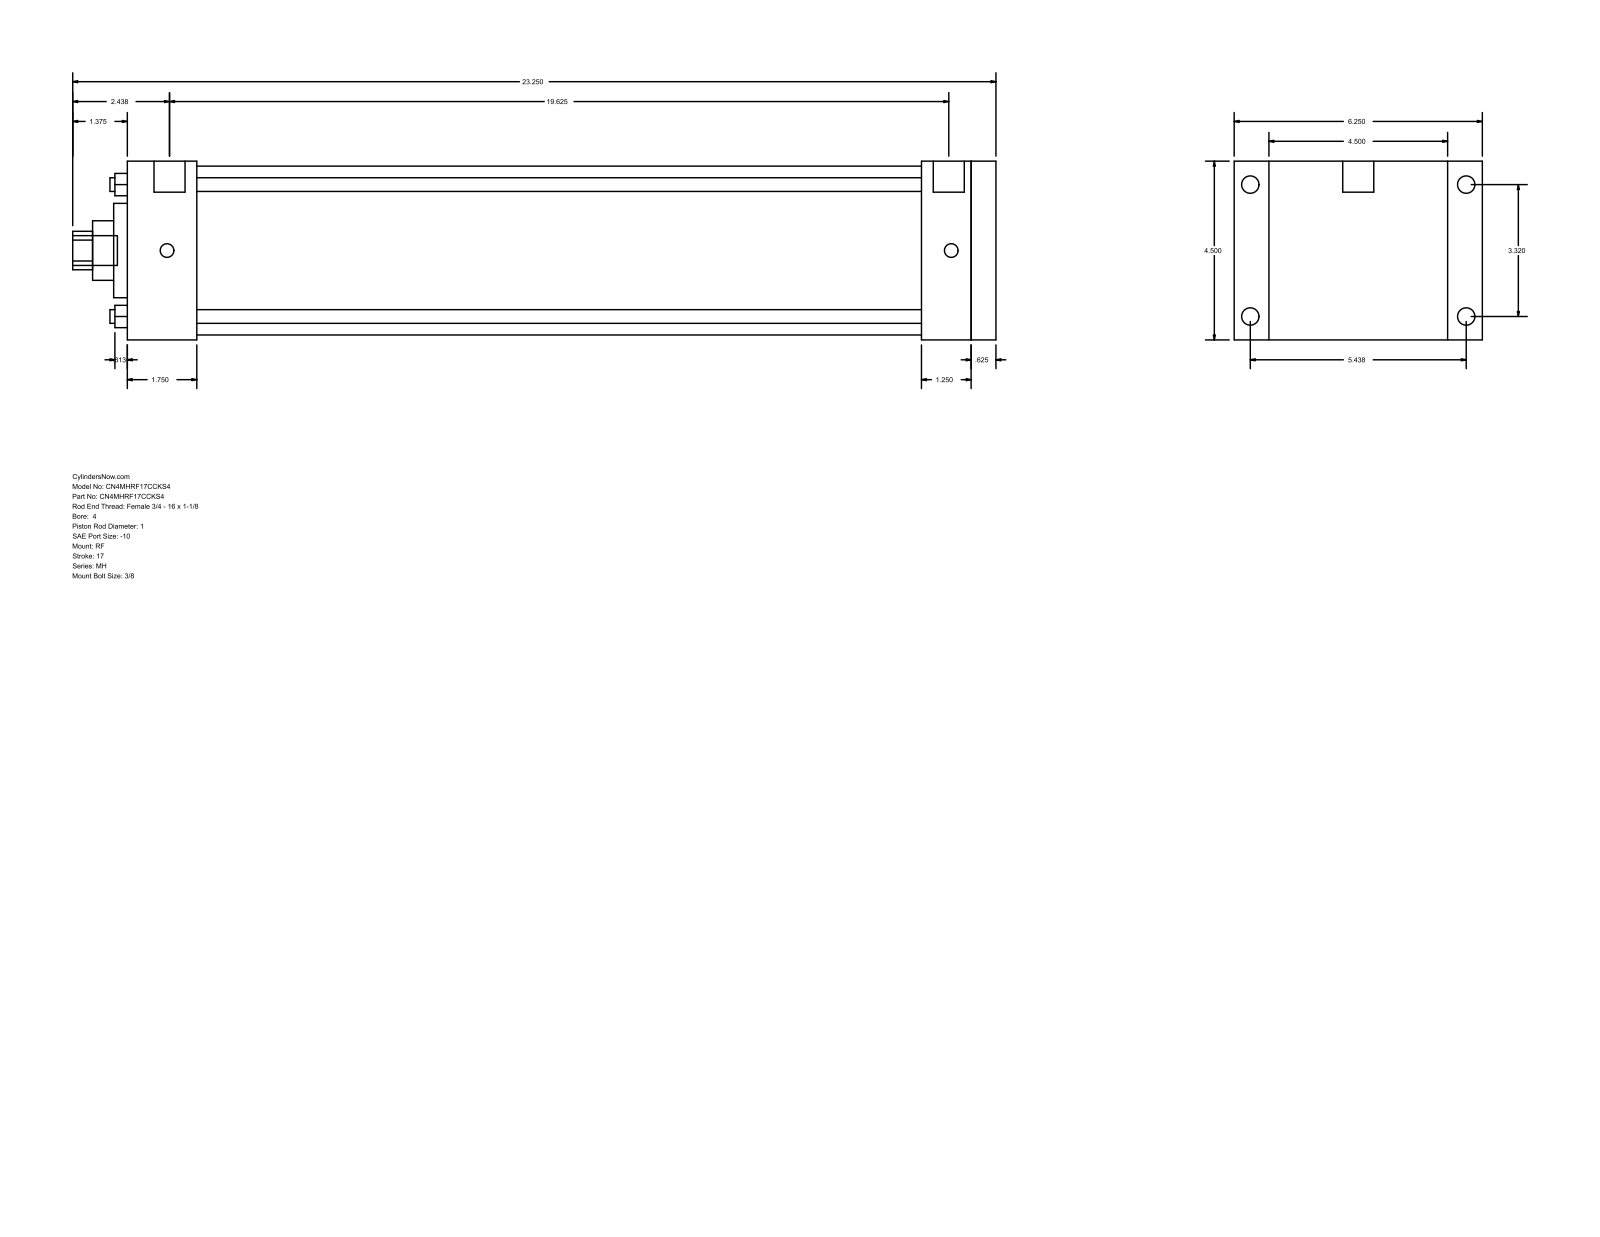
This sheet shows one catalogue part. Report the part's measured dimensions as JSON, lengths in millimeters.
{"part_name": "MH_RF__0400_1", "step_written_by": "GSSL Pune (CONFIG_CONTROL_DESIGN)", "units": "millimeters", "bodies": {"solids": 0, "faces": 94, "planar": 65, "cylindrical": 29, "other": 0}, "overall_size": [590.55, 158.75, 114.3], "round_holes": [[8.76, 4], [25.4, 1], [38.1, 1], [60.33, 1], [107.95, 1]], "round_bosses_or_shafts": [[11.13, 4], [8.73, 4], [19.84, 2], [19.05, 1]], "partial_cylinders_radius": [[12.29, 1]], "face_to_face_distances": [114.3, 555.63, 539.75, 15.88, 47.63, 44.46, 495.29, 511.17, 508, 463.54], "hole_center_spacings": [59.62, 84.32, 119.25]}
